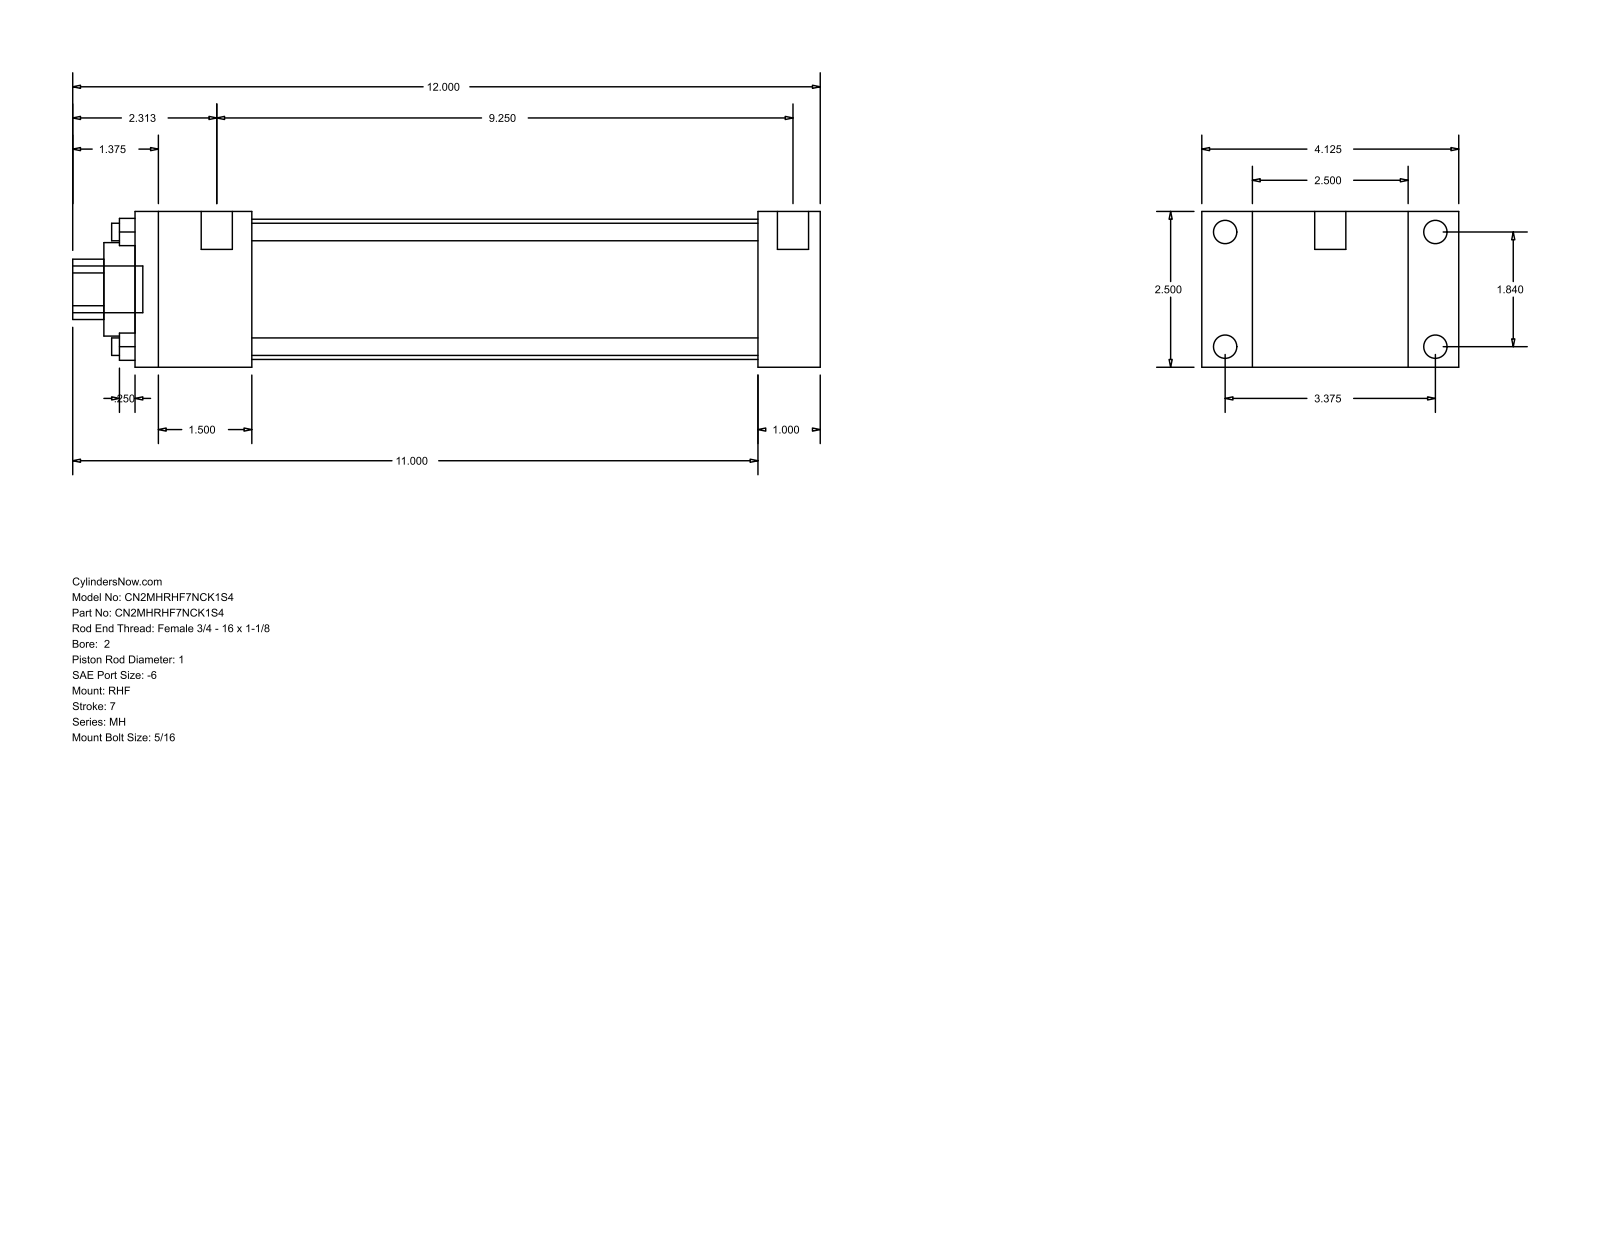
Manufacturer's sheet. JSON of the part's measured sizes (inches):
{"part_name": "MH_RHF__0200_1", "step_written_by": "GSSL Pune (CONFIG_CONTROL_DESIGN)", "units": "inches", "bodies": {"solids": 0, "faces": 88, "planar": 60, "cylindrical": 28, "other": 0}, "overall_size": [12, 4.125, 2.5], "round_holes": [[0.281, 4], [1, 1], [1.5, 1], [2.25, 1]], "round_bosses_or_shafts": [[0.375, 4], [0.219, 4], [0.5, 2], [0.75, 1]], "partial_cylinders_radius": [[0.484, 1]], "face_to_face_distances": [2.5, 1, 0.813, 3.313, 11, 10, 4.125, 1.875, 8.125, 9.125], "hole_center_spacings": [1.301, 1.84, 2.602]}
